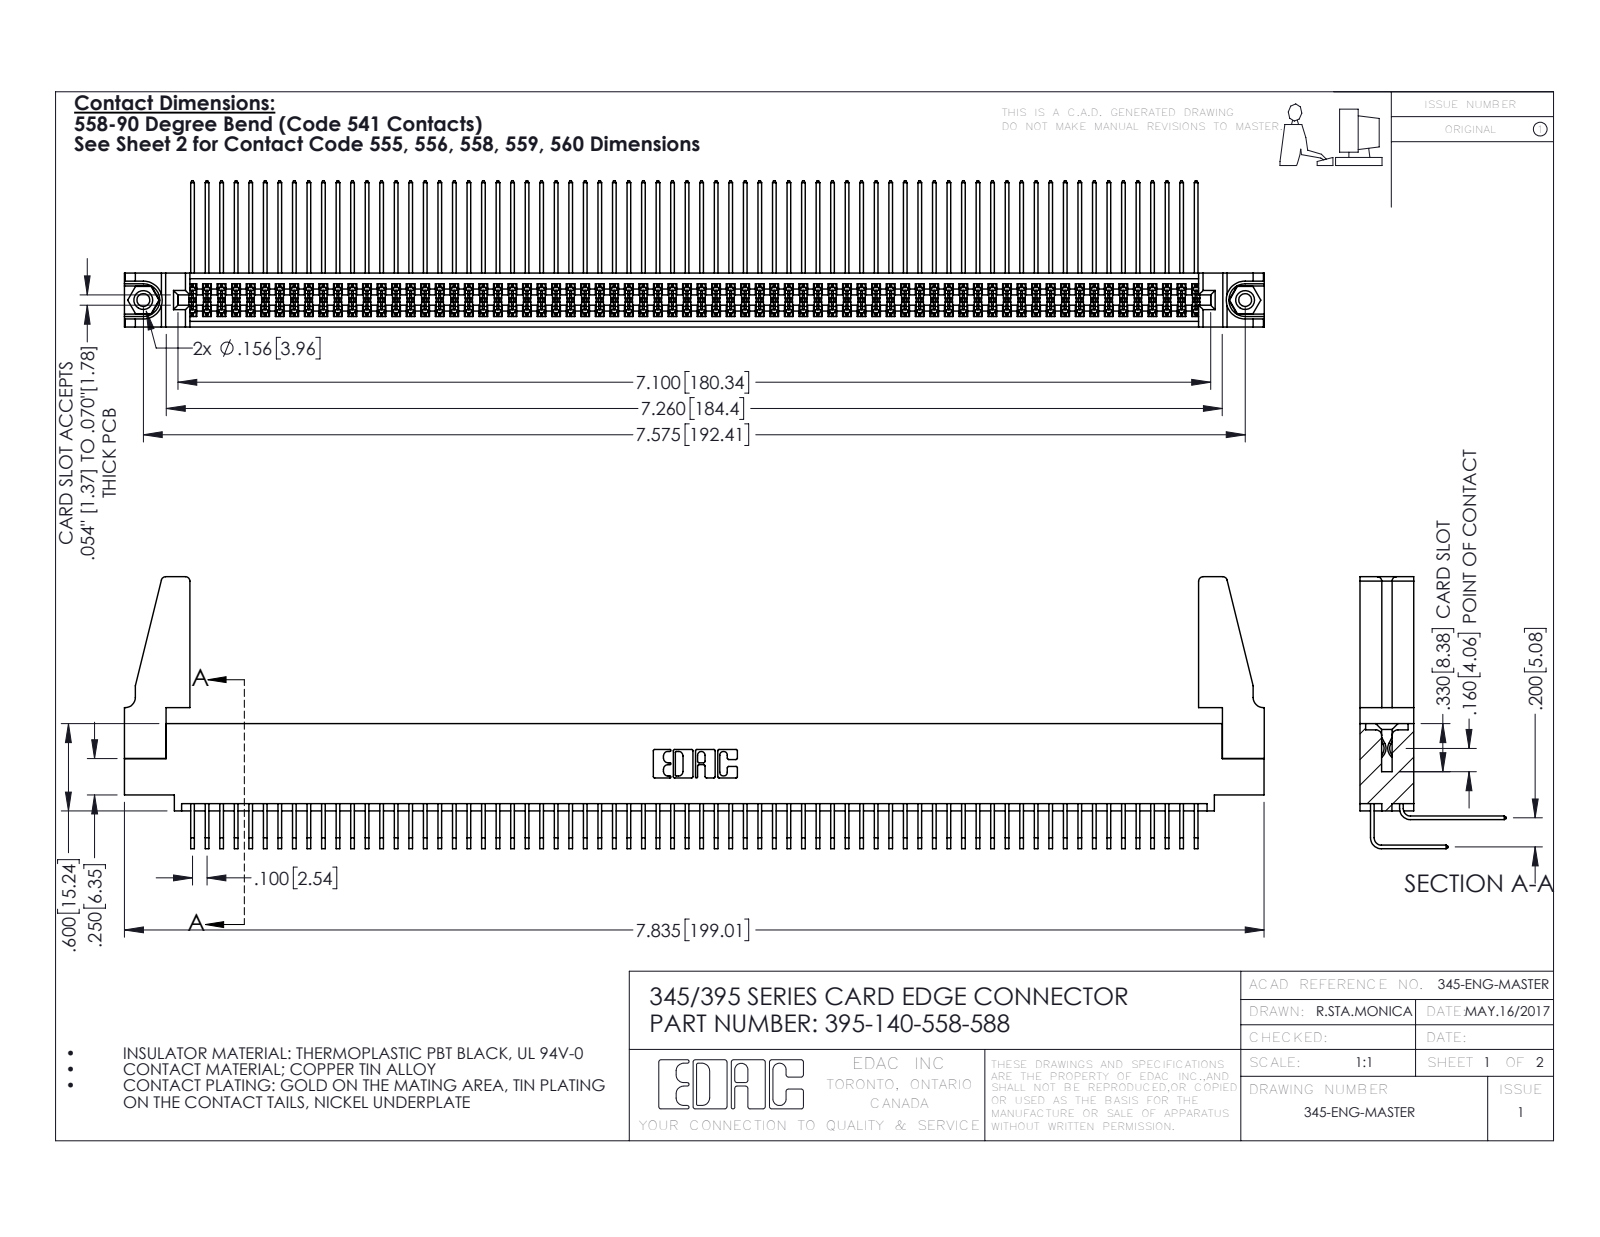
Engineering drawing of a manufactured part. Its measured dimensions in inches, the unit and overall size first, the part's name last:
Units: inches
Overall size (bounding box): 7.836 × 1.869 × 1.005
Round holes (diameter × count): ⌀0.089 ×2, ⌀0.125 ×2, ⌀0.156 ×2, ⌀0.064 ×1
Round bosses / shafts (diameter × count): ⌀0.155 ×2
Partial cylindrical surfaces — rounded edges, fillets, slot ends (radius × count): R0.006 ×279, R0.01 ×22, R0.03 ×8, R0.007 ×6, R0.031 ×6, R0.026 ×3, R0.014 ×2, R0.019 ×2
Main face-to-face distances: 0.072, 0.298, 0.2, 0.37, 0.098, 0.272, 0.025, 0.225, 0.025, 0.175
Hole centre spacings: 0.27, 7.339, 7.575
Volume: 1.439 in³ · Surface area: 58.29 in²
Bodies: 145 solids, 7534 faces (5056 planar, 2462 cylindrical, 16 other)
Part name (STEP PRODUCT): 395-140-558-588; 345-250-001_345-250-001-102; 345-292-001_558 Tail - 2; 345 Part_0.110 Offset - 0.156 Dia-TH (+2 more)
STEP written by: SolidWorks 2016 (CONFIG_CONTROL_DESIGN)
